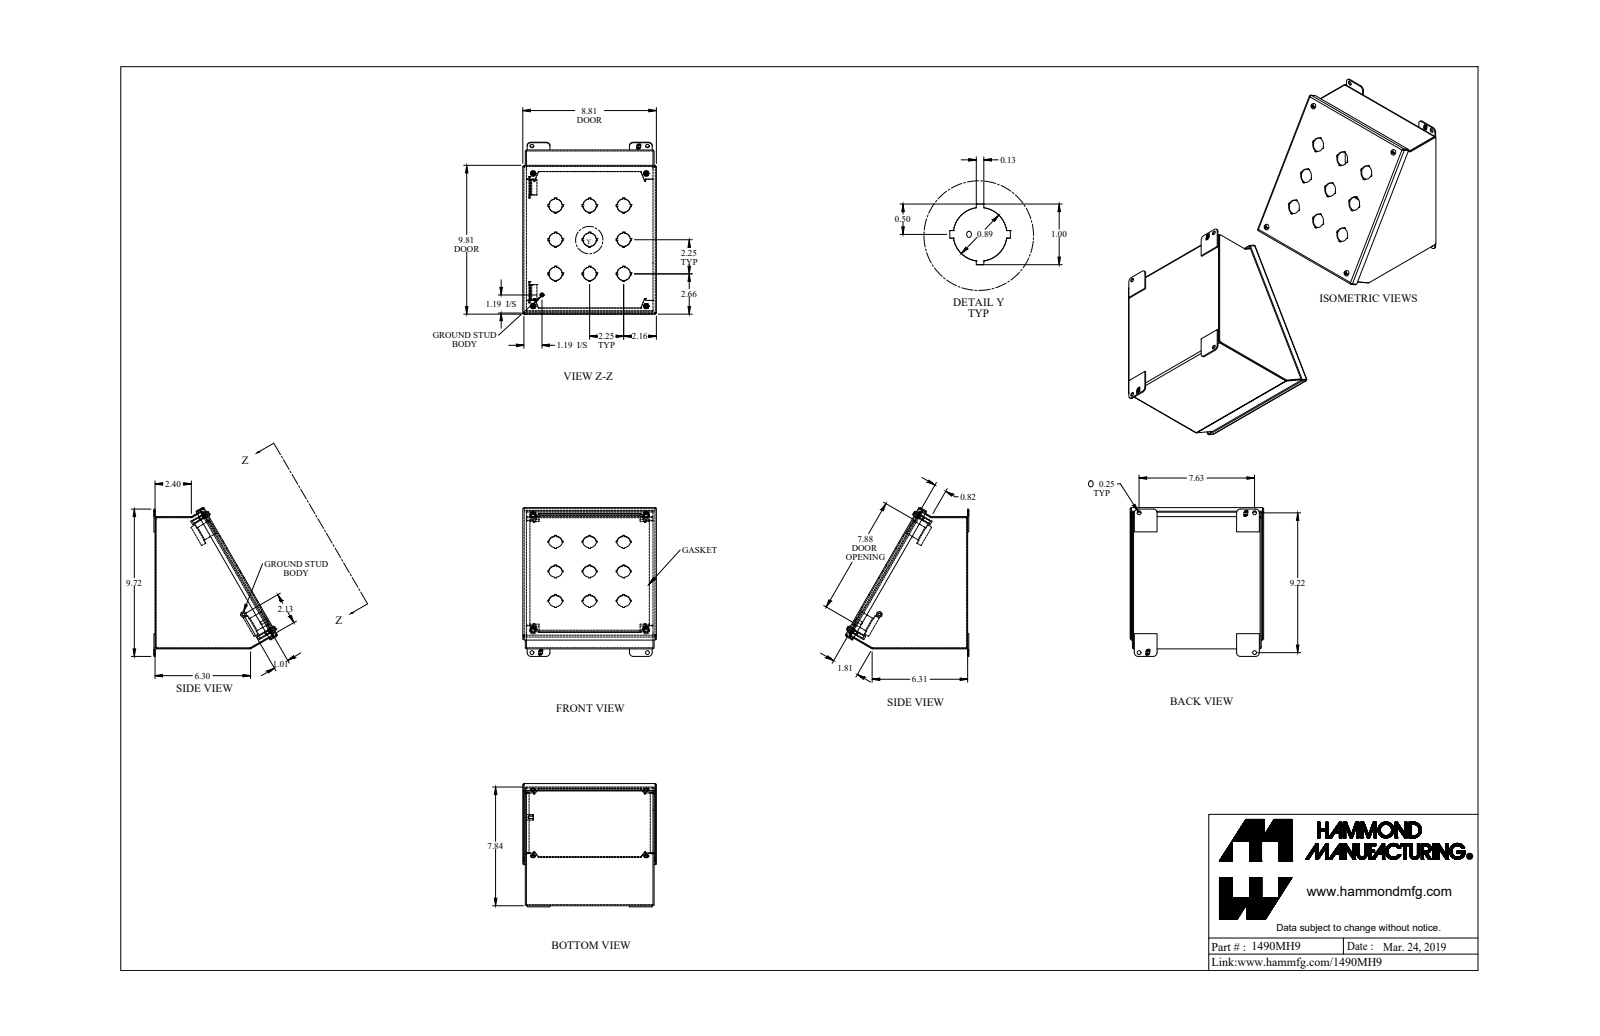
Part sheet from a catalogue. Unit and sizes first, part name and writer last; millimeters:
Units: millimetres
Overall size (bounding box): 249.9 × 223.8 × 207.7
Round holes (diameter × count): ⌀6.4 ×8, ⌀22.2 ×5, ⌀4 ×4, ⌀22.2 ×4, ⌀3 ×1, ⌀3.5 ×1, ⌀4 ×1
Round bosses / shafts (diameter × count): ⌀9.9 ×4, ⌀7 ×4, ⌀4.8 ×4, ⌀3.8 ×4, ⌀9.5 ×1, ⌀7.4 ×1
Partial cylindrical surfaces — rounded edges, fillets, slot ends (radius × count): R2.7 ×18, R0.9 ×12, R0.7 ×9, R2.2 ×9, R6.4 ×8, R3.2 ×4, R4.1 ×4, R4.3 ×4
Main face-to-face distances: 1.8, 214.1, 212.2, 215.9, 219.6, 221.4, 217.8, 4, 243.4, 239.5
Hole centre spacings: 127.8, 57.2, 109, 114.3, 222.3, 226.7, 188.2, 65.8
Volume: 454 400 mm³ · Surface area: 511 000 mm²
Bodies: 26 solids, 838 faces (591 planar, 209 cylindrical, 38 other)
Part name (STEP PRODUCT): 1490MH9_Default
STEP written by: SolidWorks 2019 (CONFIG_CONTROL_DESIGN)
